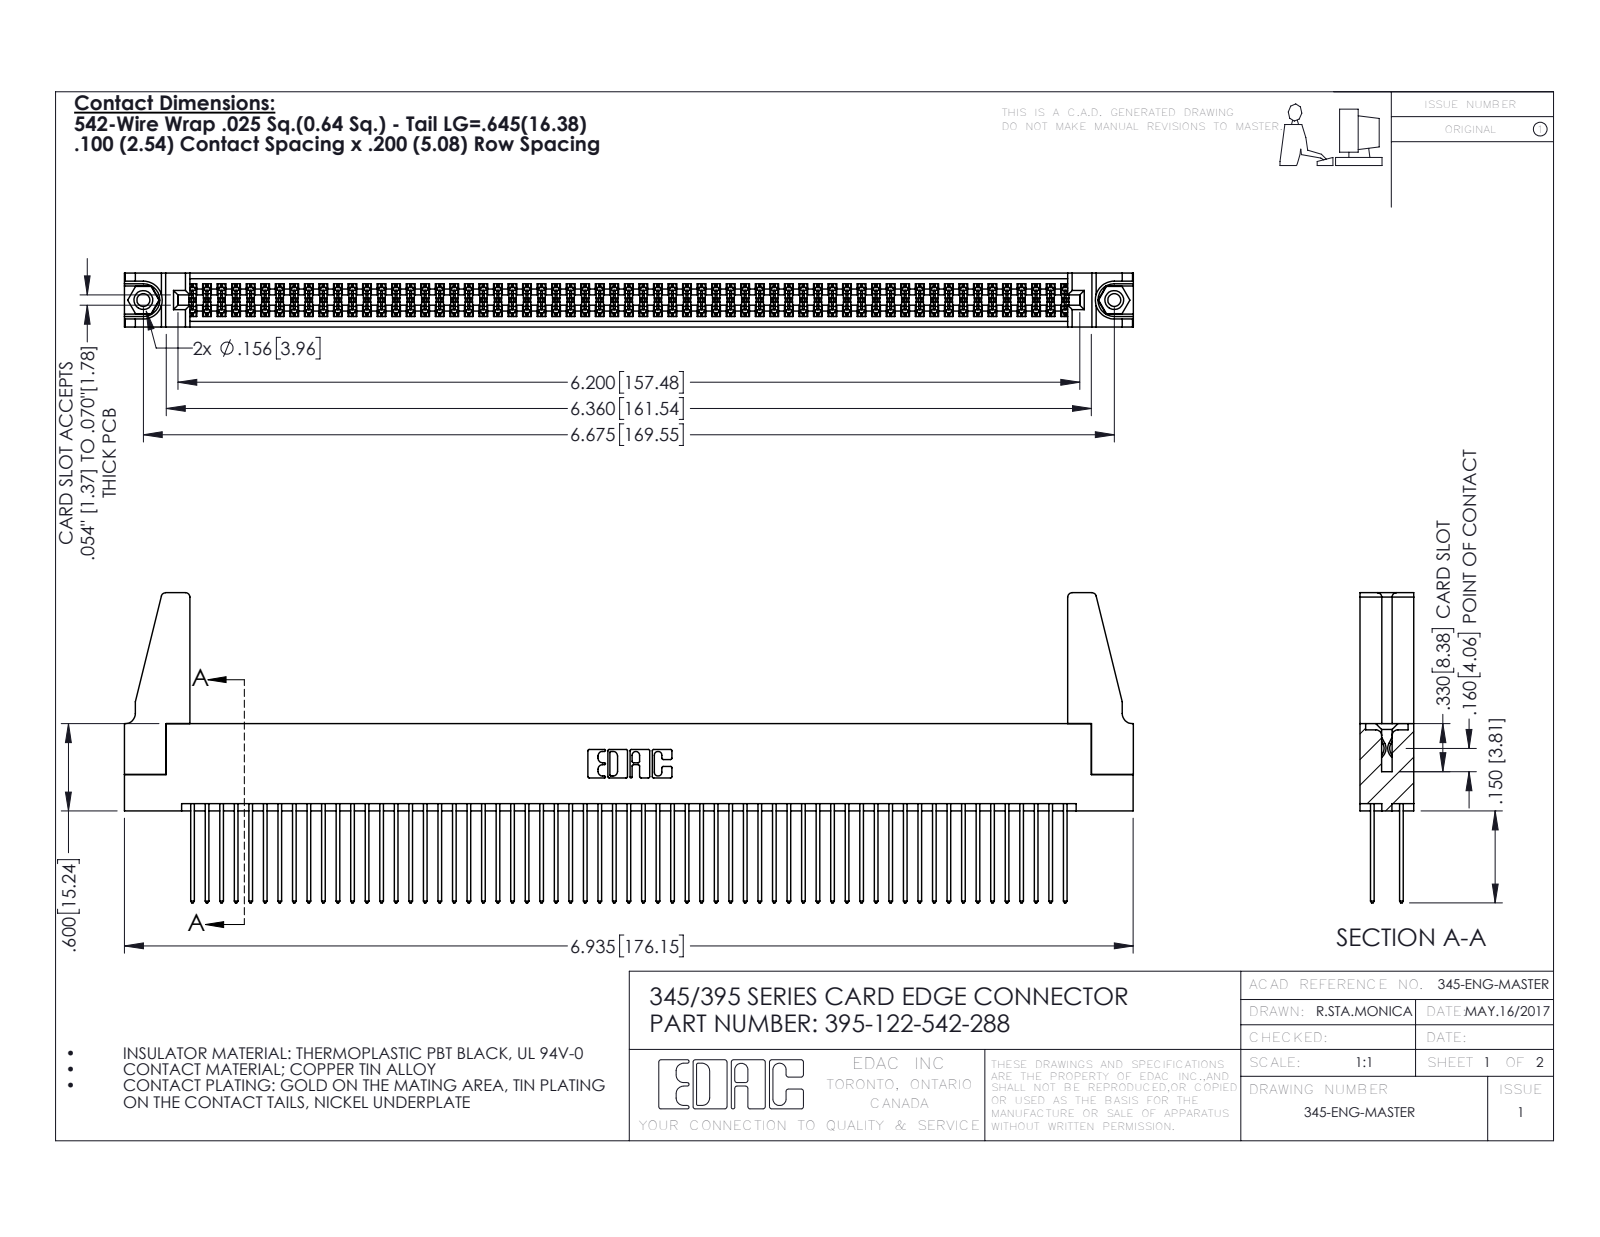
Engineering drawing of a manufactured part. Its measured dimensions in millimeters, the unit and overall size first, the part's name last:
Units: millimetres
Overall size (bounding box): 176.2 × 54.2 × 9.4
Round holes (diameter × count): ⌀2.3 ×2, ⌀3.2 ×2, ⌀4 ×2, ⌀1.6 ×1
Round bosses / shafts (diameter × count): ⌀3.9 ×2
Partial cylindrical surfaces — rounded edges, fillets, slot ends (radius × count): R0.2 ×183, R0.3 ×122, R0.3 ×22, R0.8 ×8, R0.2 ×6, R0.8 ×6, R0.7 ×3, R0.4 ×2
Main face-to-face distances: 1.8, 7.6, 5.1, 2.5, 6.9, 0.6, 9.4, 5.7, 4.4, 3.8
Hole centre spacings: 6.9, 163.6, 169.5
Volume: 21 110 mm³ · Surface area: 32 550 mm²
Bodies: 127 solids, 6350 faces (4178 planar, 2156 cylindrical, 16 other)
Part name (STEP PRODUCT): 345 Part_Flush Mounting Lugs - 0.156 Dia-TH; 345-292-001_345-293-142; 345-250-001_345-250-001-102; 345-220-078_345-220-088 (+1 more)
STEP written by: SolidWorks 2016 (CONFIG_CONTROL_DESIGN)
